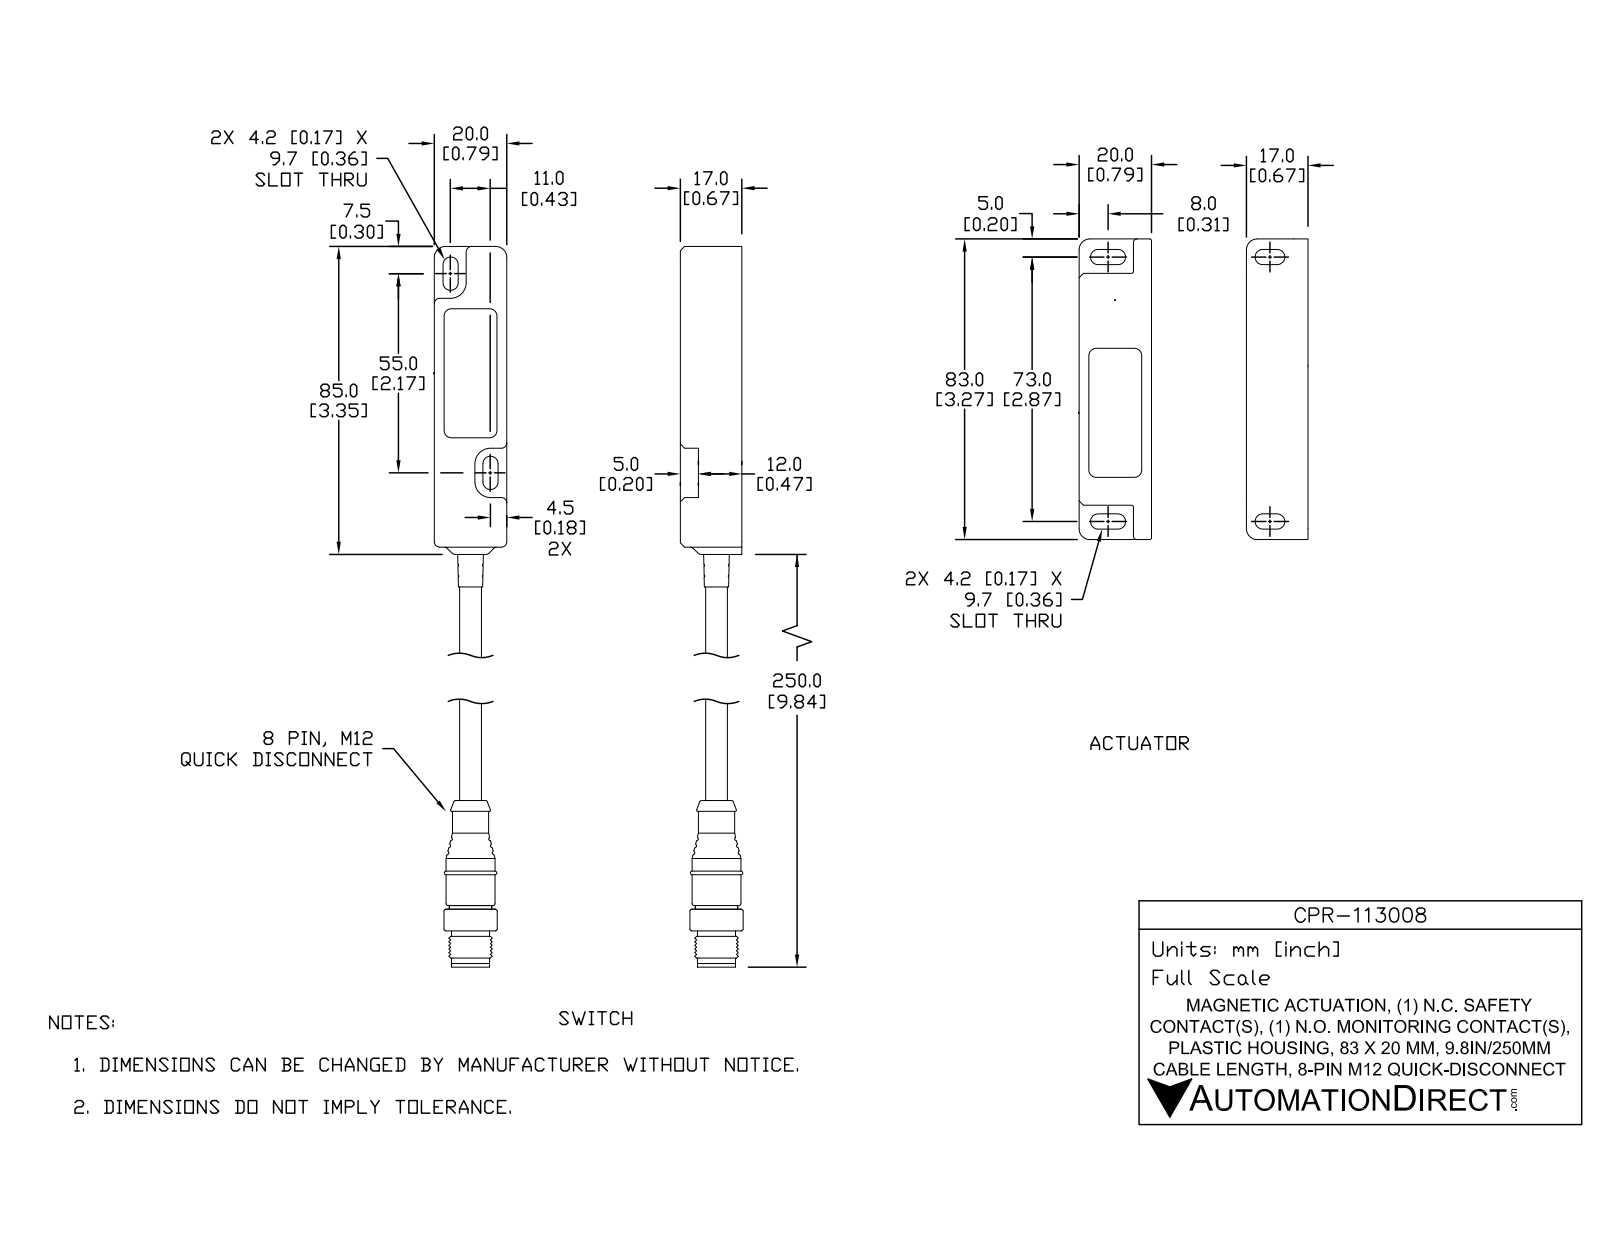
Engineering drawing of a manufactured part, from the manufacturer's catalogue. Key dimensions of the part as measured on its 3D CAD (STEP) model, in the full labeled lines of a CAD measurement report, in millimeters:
Part name (STEP PRODUCT): CPR-113008_1; CPR-113008; CPR-113008_2
STEP written by: SolidWorks 2017 (AUTOMOTIVE_DESIGN)
Units: millimetres
Bodies: 4 solids, 194 faces (77 planar, 69 cylindrical, 48 other)
Overall size (bounding box): 182.1 × 41 × 17
Volume: 53 140 mm³ · Surface area: 16 170 mm²
Round bosses / shafts (diameter × count): ⌀6 ×1
Partial cylindrical surfaces — rounded edges, fillets, slot ends (radius × count): R2.1 ×12, R1 ×10, R0.5 ×8, R2 ×8, R1.5 ×6, R3 ×6, R0.7 ×3, R4.3 ×3
Main face-to-face distances: 21, 20, 17, 41, 16.7, 1, 5, 12, 9.5, 73.5
